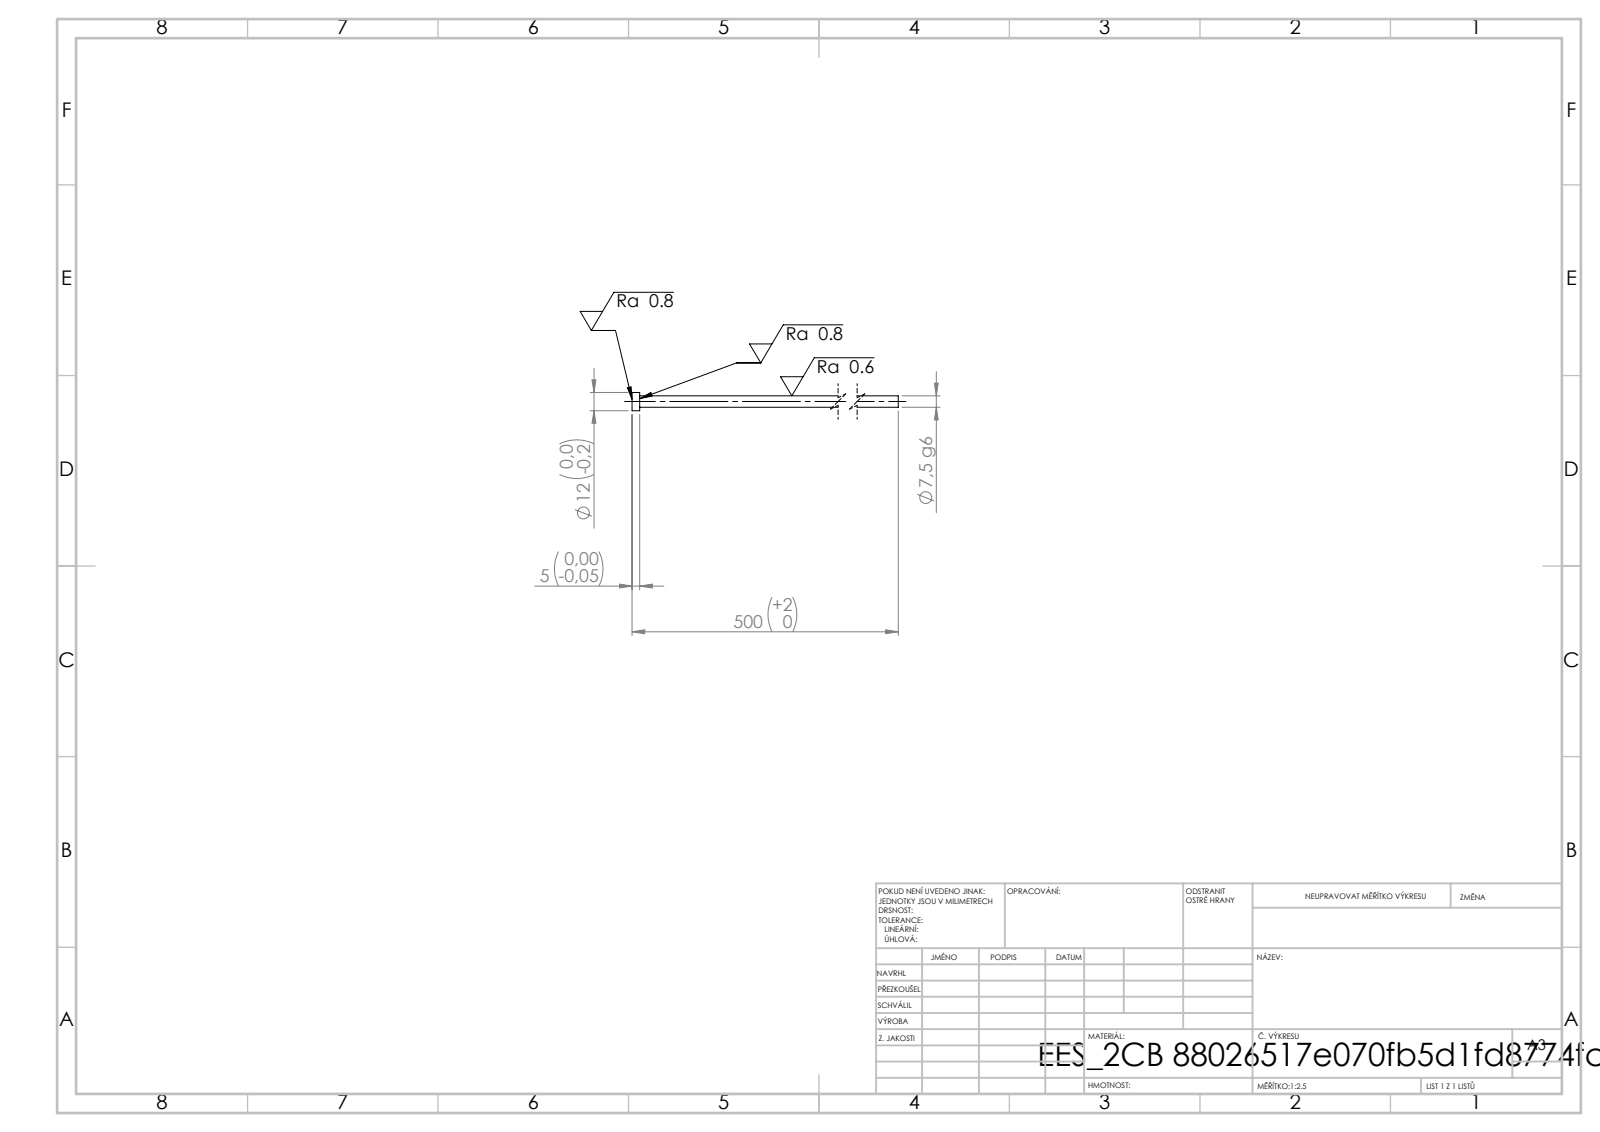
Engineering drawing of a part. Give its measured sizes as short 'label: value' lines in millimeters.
written by: SolidWorks 2019 (CONFIG_CONTROL_DESIGN)
unit: mm
bodies: 1 solid, 7 faces (3 planar, 4 cylindrical, 0 other)
size: 500 × 12 × 12
volume: 22 434 mm³; area: 12 078 mm²
bosses: 1× ⌀12, 1× ⌀7.5
face distances: 5, 500, 495
